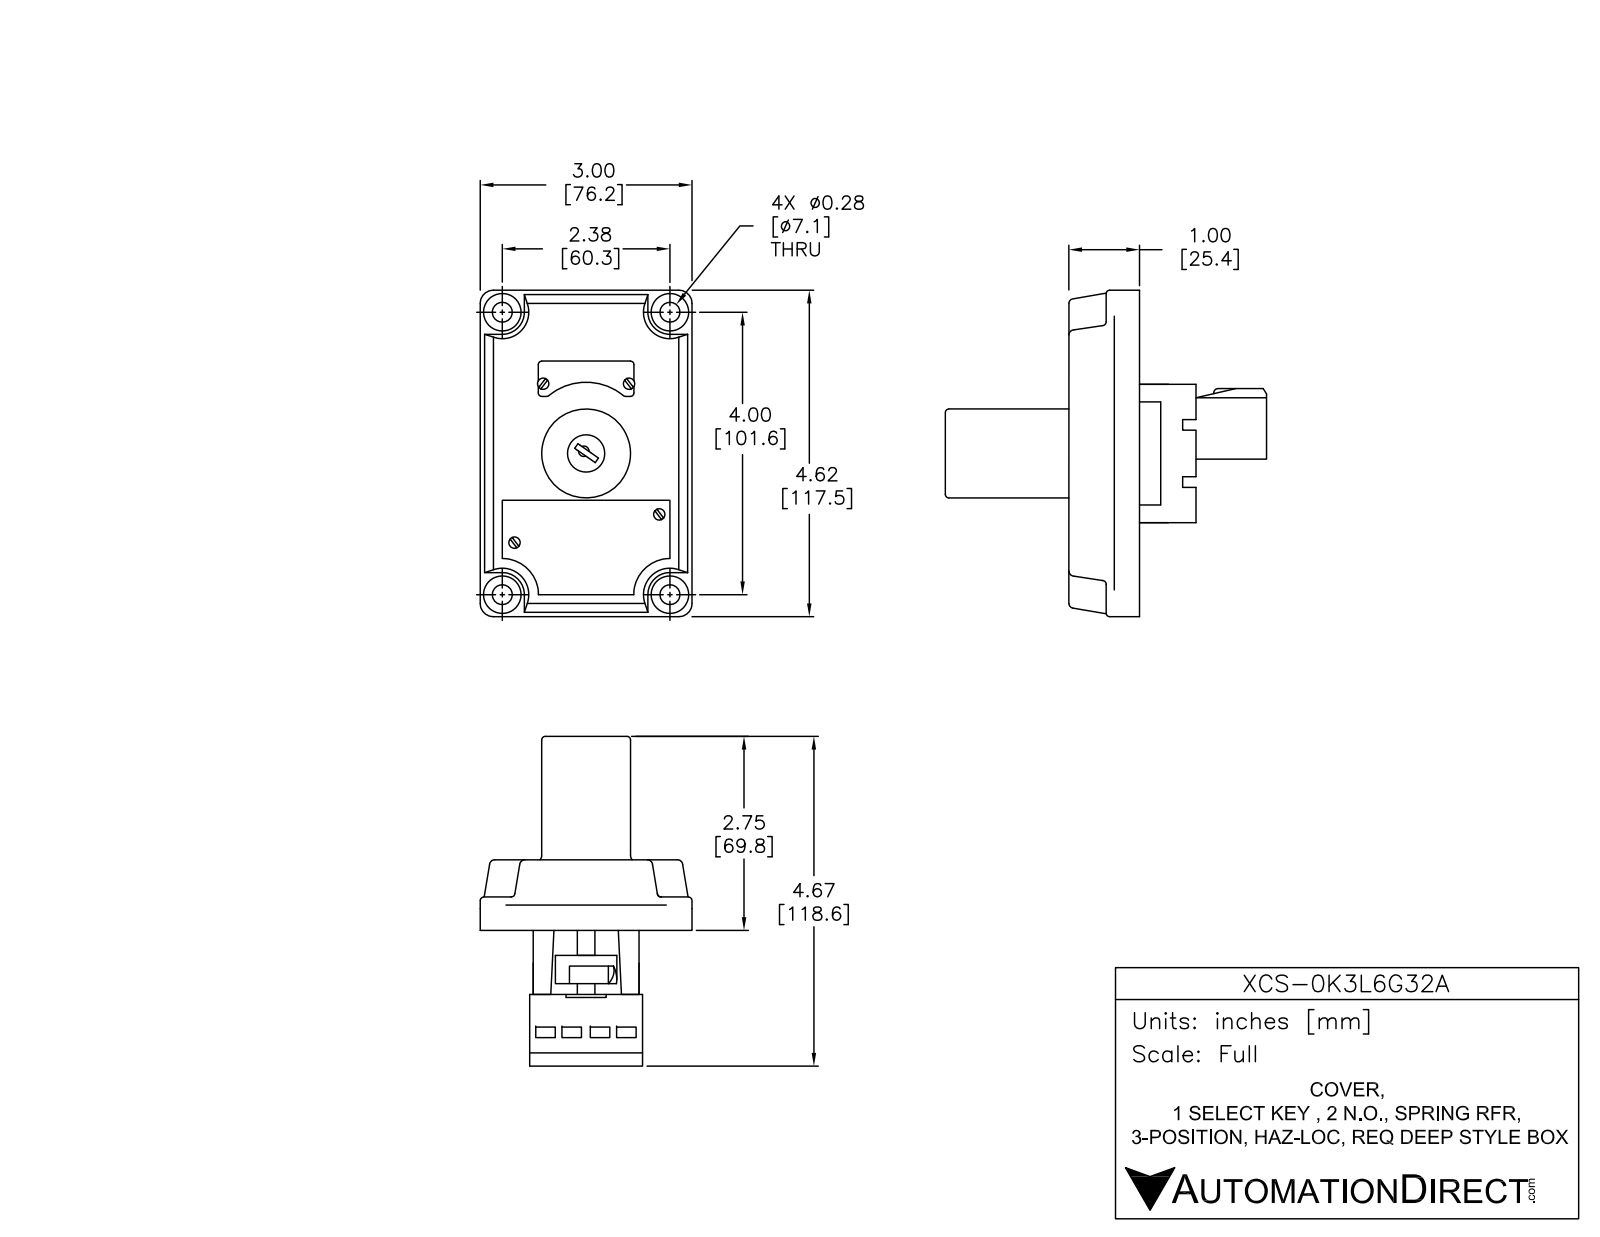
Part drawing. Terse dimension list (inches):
name: XCS-0K3L6G32A
written by: SolidWorks 2015 (AUTOMOTIVE_DESIGN)
unit: in
bodies: 10 solids, 476 faces (177 planar, 169 cylindrical, 130 other)
size: 4.63 × 4.191 × 3.1
volume: 14.02 in³; area: 90.43 in²
holes: 4× ⌀0.262, 4× ⌀0.27, 1× ⌀0.528
bosses: 6× ⌀0.13, 4× ⌀0.457, 4× ⌀0.25, 1× ⌀1.26
rounds: 28× R0.01, 10× R0.05, 8× R0.02, 8× R0.055, 8× R0.118, 4× R0.094, 4× R0.1, 4× R0.38
face distances: 0.525, 0.5, 1.025, 0.445, 0.945, 1.47, 0.689, 0.256, 0.189, 1.214
hole spacings: 2.327, 0.402, 0.803, 2.38, 4, 4.655, 0.399, 0.401
